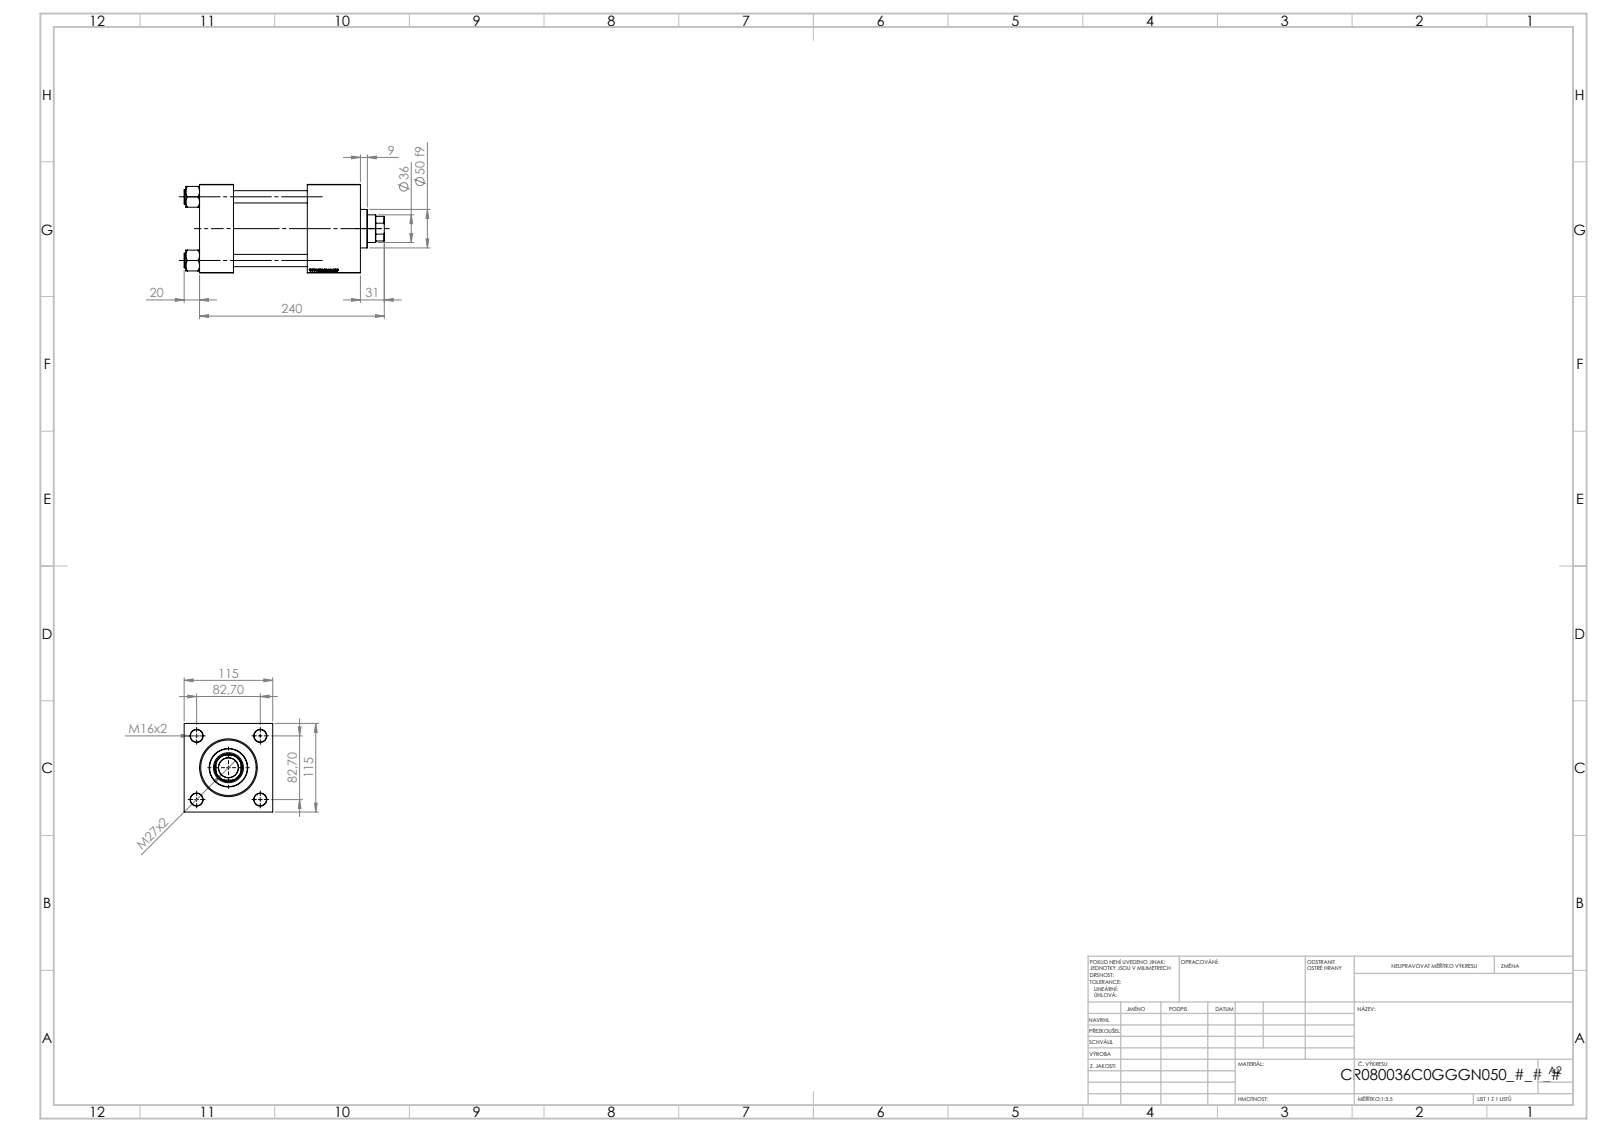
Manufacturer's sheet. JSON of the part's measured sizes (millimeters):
{"part_name": "V215CR_VCP_C; V215CR_C_TYCINKA; V215_VC_A; NUT_M5_C (+1 more)", "step_written_by": "SolidWorks 2019 (CONFIG_CONTROL_DESIGN)", "units": "millimeters", "bodies": {"solids": 11, "faces": 1197, "planar": 574, "cylindrical": 87, "other": 536}, "overall_size": [260, 115, 115], "volume_mm3": 1864000, "surface_area_mm2": 293512, "round_holes": [[16, 4], [7, 2], [26.44, 2], [35, 2], [25.5, 1], [36, 1], [39, 1], [61, 1], [72, 1], [80, 1]], "round_bosses_or_shafts": [[19, 4], [86, 1], [50, 1]], "partial_cylinders_radius": [[17.5, 1]], "face_to_face_distances": [115, 44, 209, 165, 69, 140, 96, 180.3, 136.3, 40.3], "hole_center_spacings": [58.48, 82.7, 116.96, 141]}
